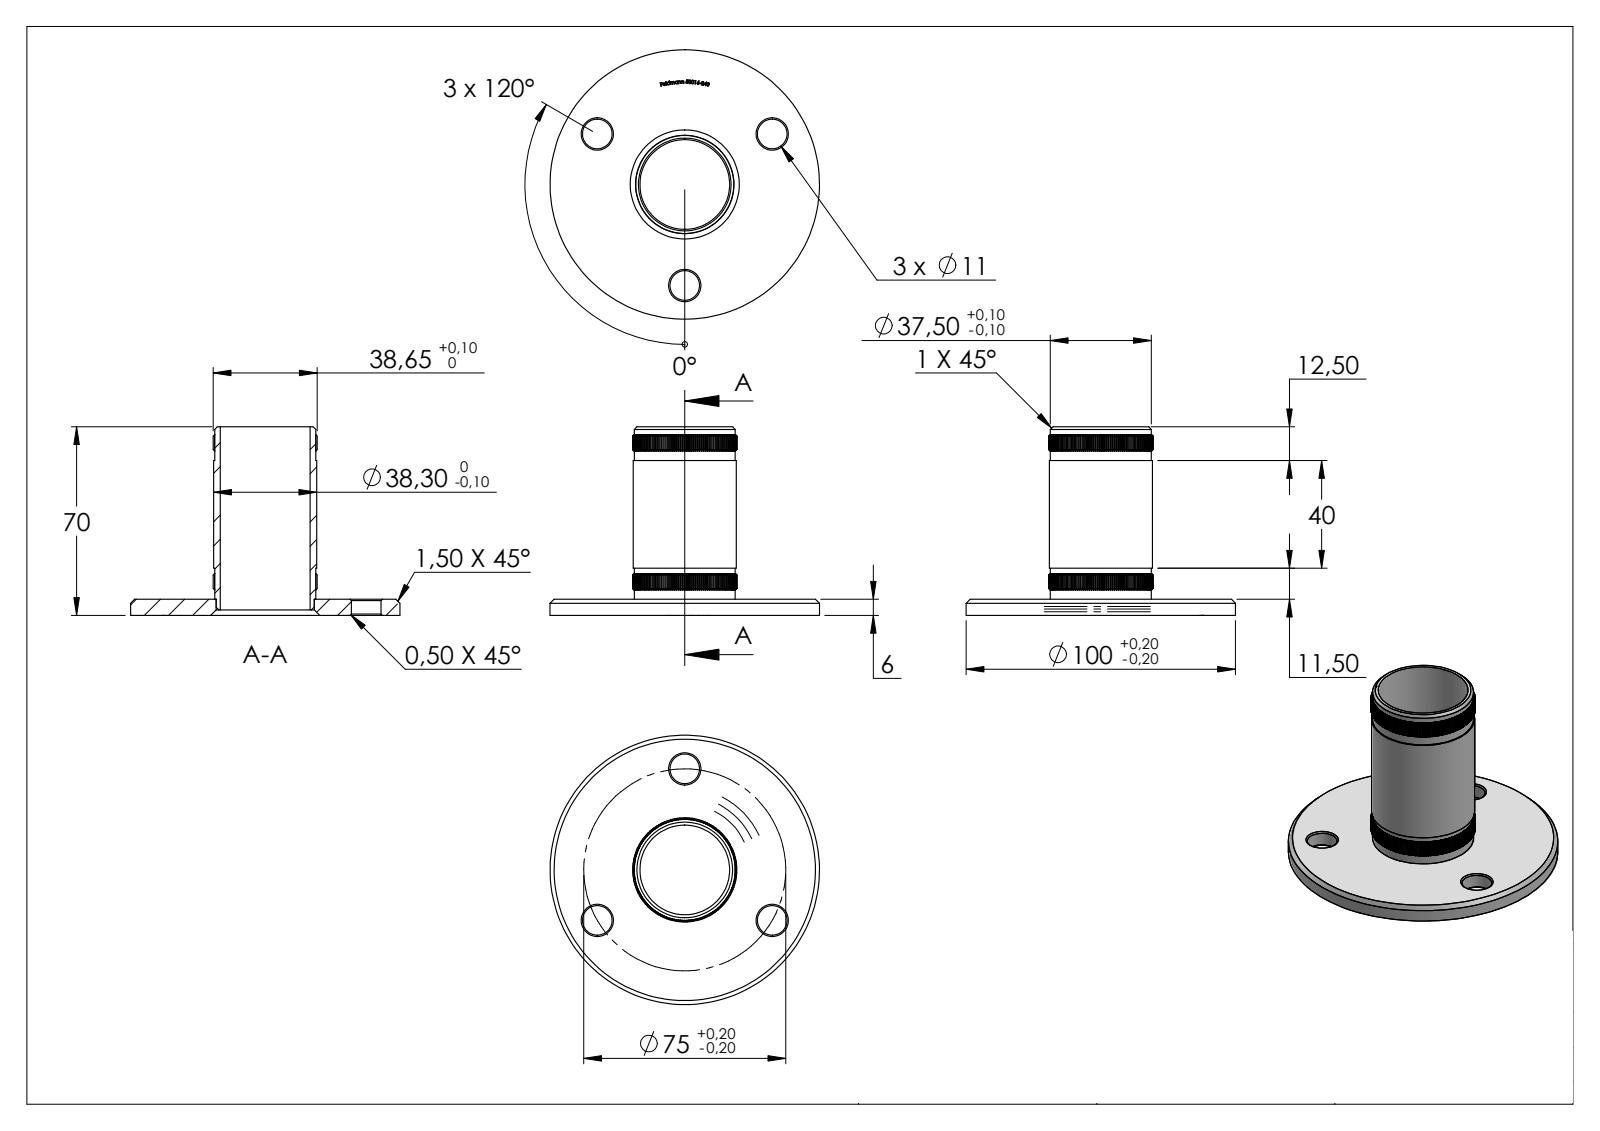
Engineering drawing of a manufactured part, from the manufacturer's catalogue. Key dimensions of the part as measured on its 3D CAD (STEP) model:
Part name (STEP PRODUCT): 500XX-240 Teil2 Konfig_50016-240 Teil2; 500XX-240 Teil2 Konfig; 50016-240; 500XX-240 Konfig_50016-240 Teil1 (+1 more)
STEP written by: SolidWorks 2015 (CONFIG_CONTROL_DESIGN)
Units: millimetres
Bodies: 2 solids, 2644 faces (1324 planar, 612 cylindrical, 708 other)
Overall size (bounding box): 100 × 100 × 70
Volume: 56 516 mm³ · Surface area: 33 010 mm²
Round holes (diameter × count): ⌀11 ×3, ⌀33.3 ×1, ⌀36.5 ×1
Round bosses / shafts (diameter × count): ⌀100 ×1, ⌀38.3 ×1, ⌀37.5 ×1, ⌀36.4 ×1
Partial cylindrical surfaces — rounded edges, fillets, slot ends (radius × count): R19.32 ×1
Main face-to-face distances: 6, 9.66, 9.68, 70, 64, 9.64, 2, 51.5, 4, 68
Hole centre spacings: 37.5, 64.95, 64.96
